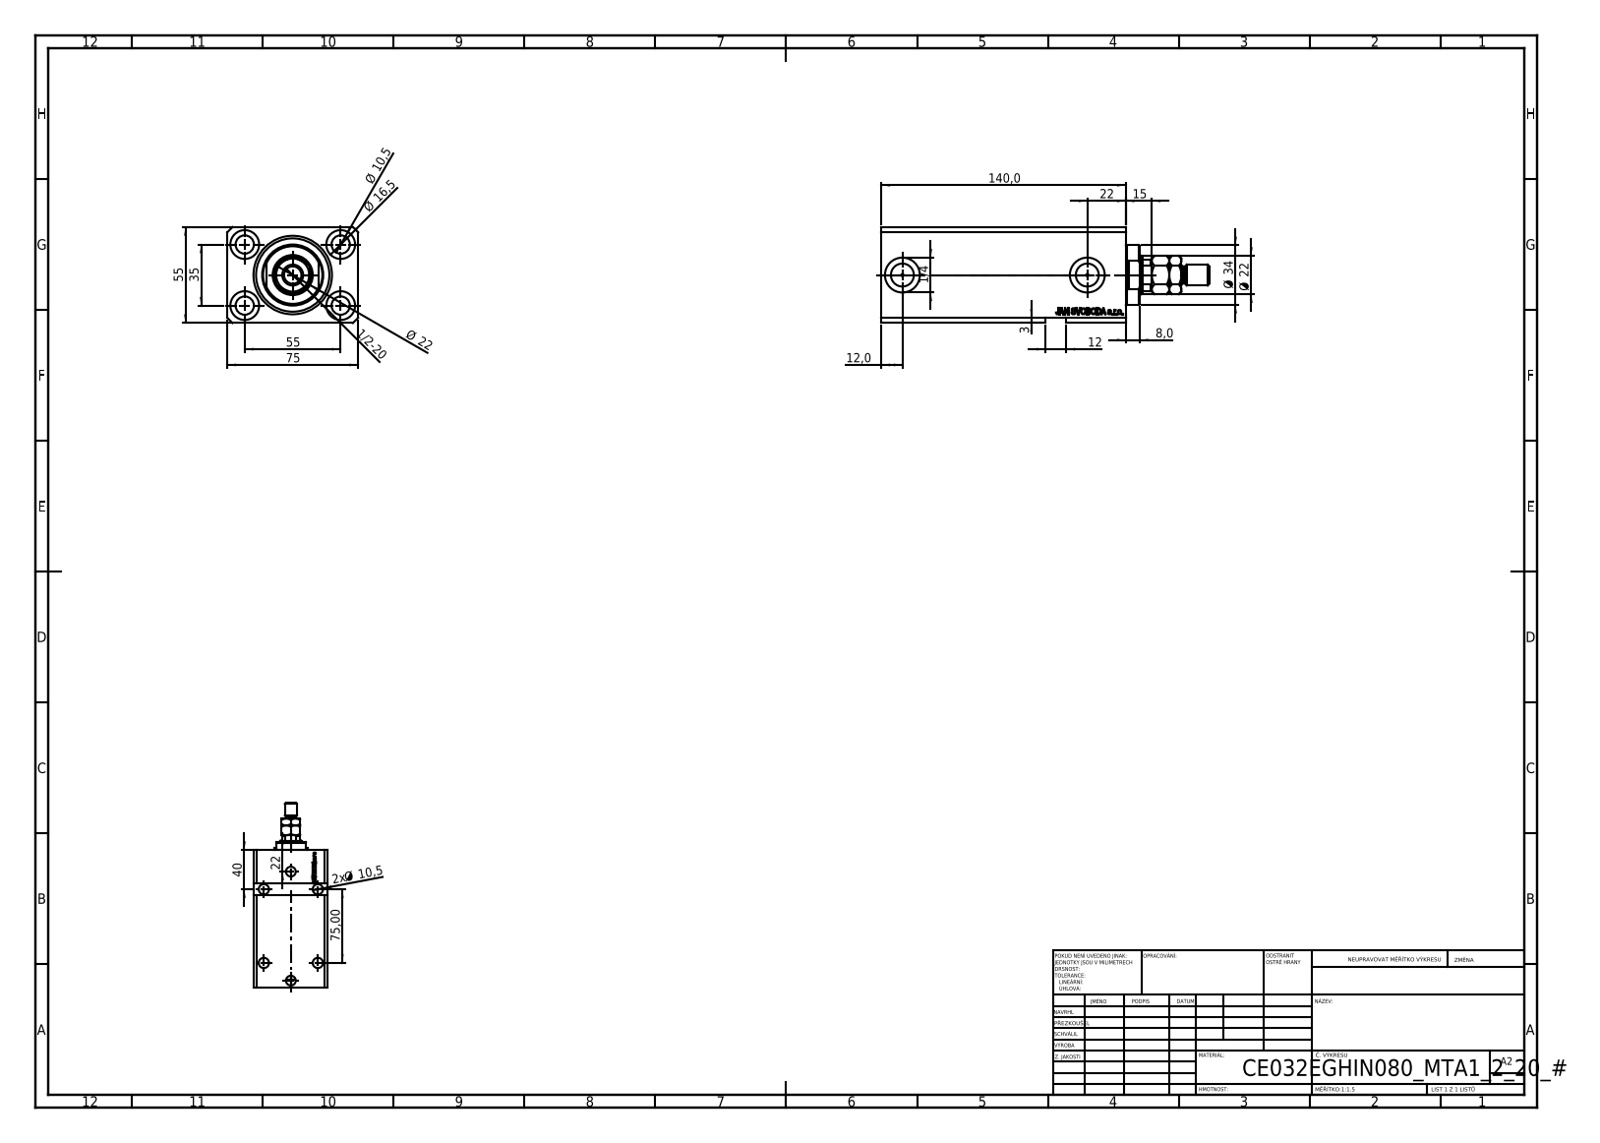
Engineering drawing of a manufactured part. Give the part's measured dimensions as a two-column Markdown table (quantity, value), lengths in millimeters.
| quantity | value |
| --- | --- |
| part name | V250CE_E_Body; MTA; V250CE_C_VCP; V250CE_VC_E |
| STEP written by | SolidWorks 2019 (CONFIG_CONTROL_DESIGN) |
| units | millimeters |
| bodies | 4 solids, 963 faces (453 planar, 108 cylindrical, 402 other) |
| overall size | 188 × 75 × 55 |
| volume | 476 184 mm³ |
| surface area | 104 344 mm² |
| round holes (diameter × count) | 10.5 × 9, 1.25 × 4, 16.5 × 4, 10 × 2, 13.16 × 2, 20 × 2, 22 × 1, 32 × 1, 45 × 1 |
| round bosses / shafts (diameter × count) | 34 × 1, 12 × 1, 10 × 1 |
| partial cylindrical surfaces (radius × count) | 10.5 × 1 |
| main face-to-face distances | 55, 75, 15, 140, 125, 9.9, 115.1, 130.1, 19, 11 |
| hole center spacings | 32.6, 32.87, 55, 96.98, 32.58, 35, 65.19, 75 |
